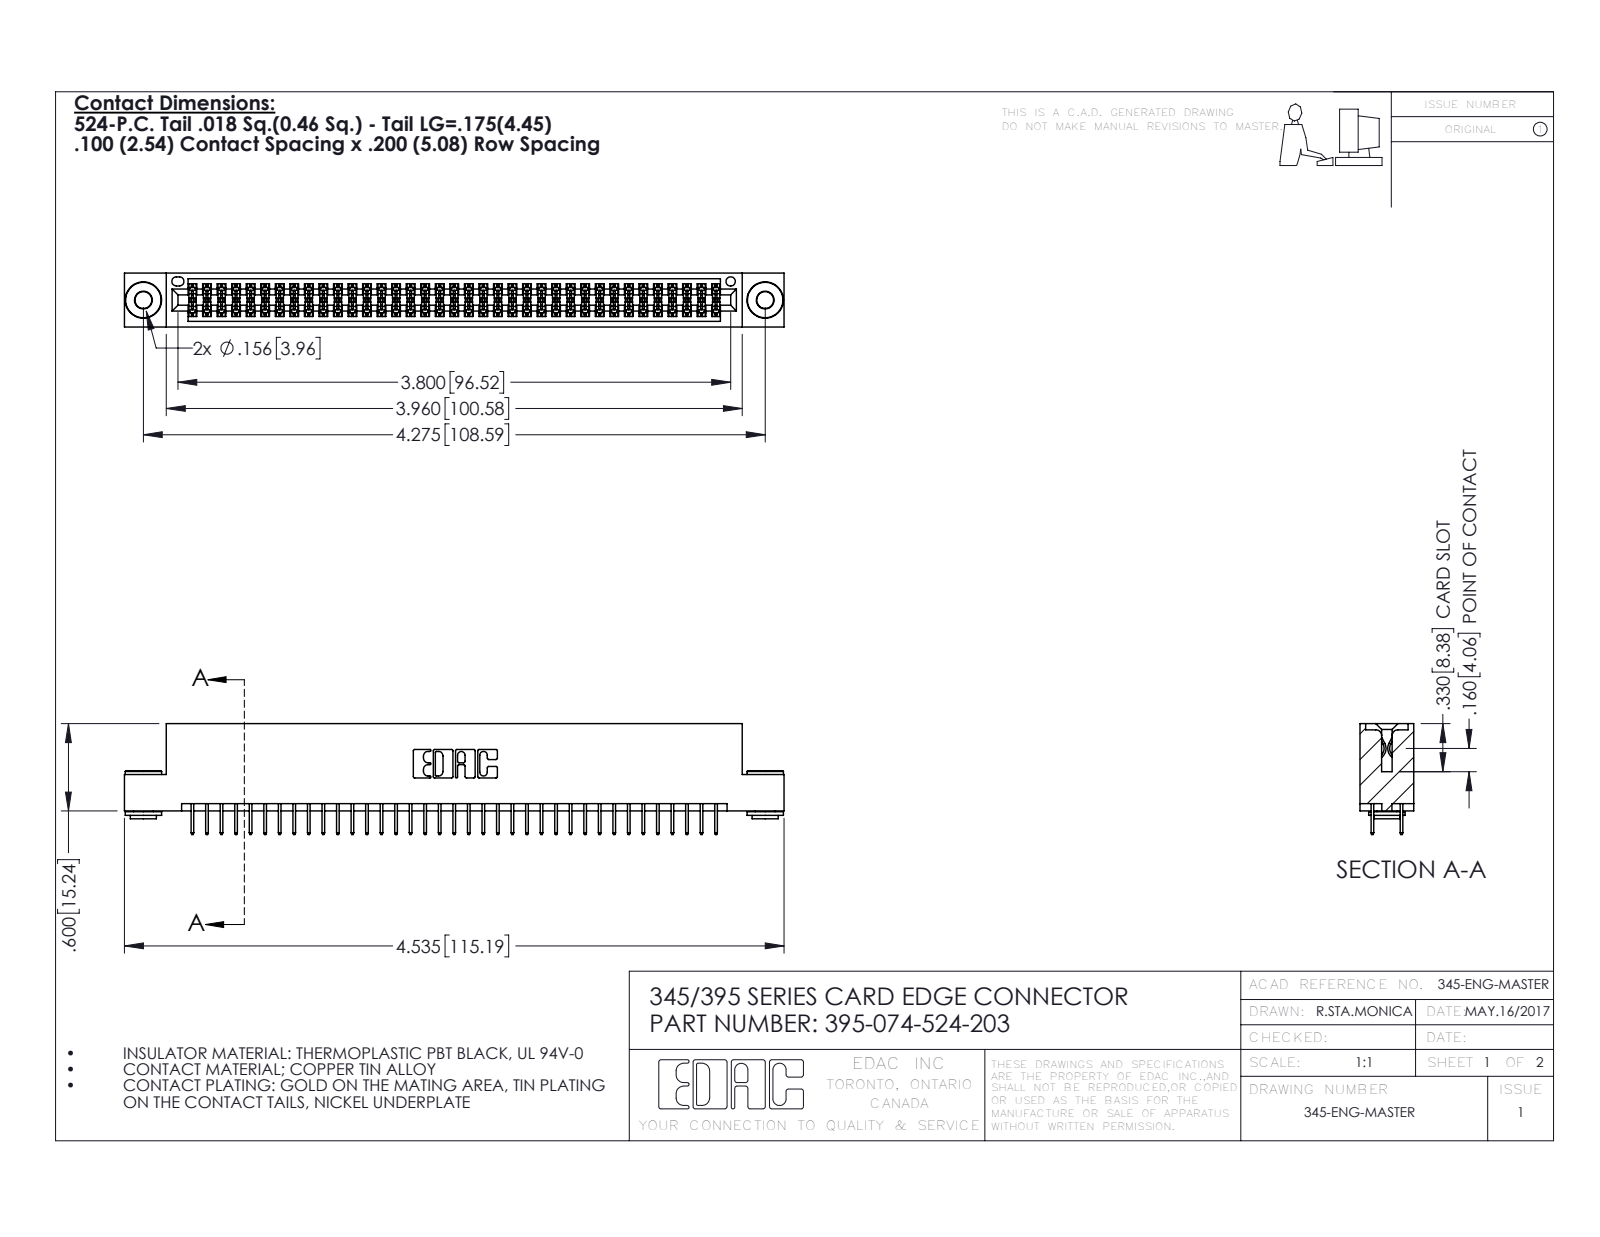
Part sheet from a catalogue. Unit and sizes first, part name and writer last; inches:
Units: inches
Overall size (bounding box): 4.535 × 0.762 × 0.37
Round holes (diameter × count): ⌀0.116 ×2, ⌀0.156 ×2, ⌀0.064 ×1
Round bosses / shafts (diameter × count): ⌀0.25 ×2, ⌀0.18 ×2, ⌀0.136 ×2
Partial cylindrical surfaces — rounded edges, fillets, slot ends (radius × count): R0.006 ×111, R0.01 ×22, R0.007 ×6, R0.031 ×6, R0.026 ×3, R0.014 ×2, R0.019 ×2, R0.022 ×2
Main face-to-face distances: 0.072, 0.298, 0.2, 0.37, 0.025, 0.098, 0.272, 0.225, 0.072, 0.175
Hole centre spacings: 0.27, 4.039, 4.275
Volume: 0.674 in³ · Surface area: 25.03 in²
Bodies: 77 solids, 4160 faces (2976 planar, 1176 cylindrical, 8 other)
Part name (STEP PRODUCT): 345 Part_Flush Mounting Lugs - 0.156 Dia-TH; 345-292-001_345-293-124; 395-074-524-203; 345-250-002_345-250-002-102
STEP written by: SolidWorks 2016 (CONFIG_CONTROL_DESIGN)
